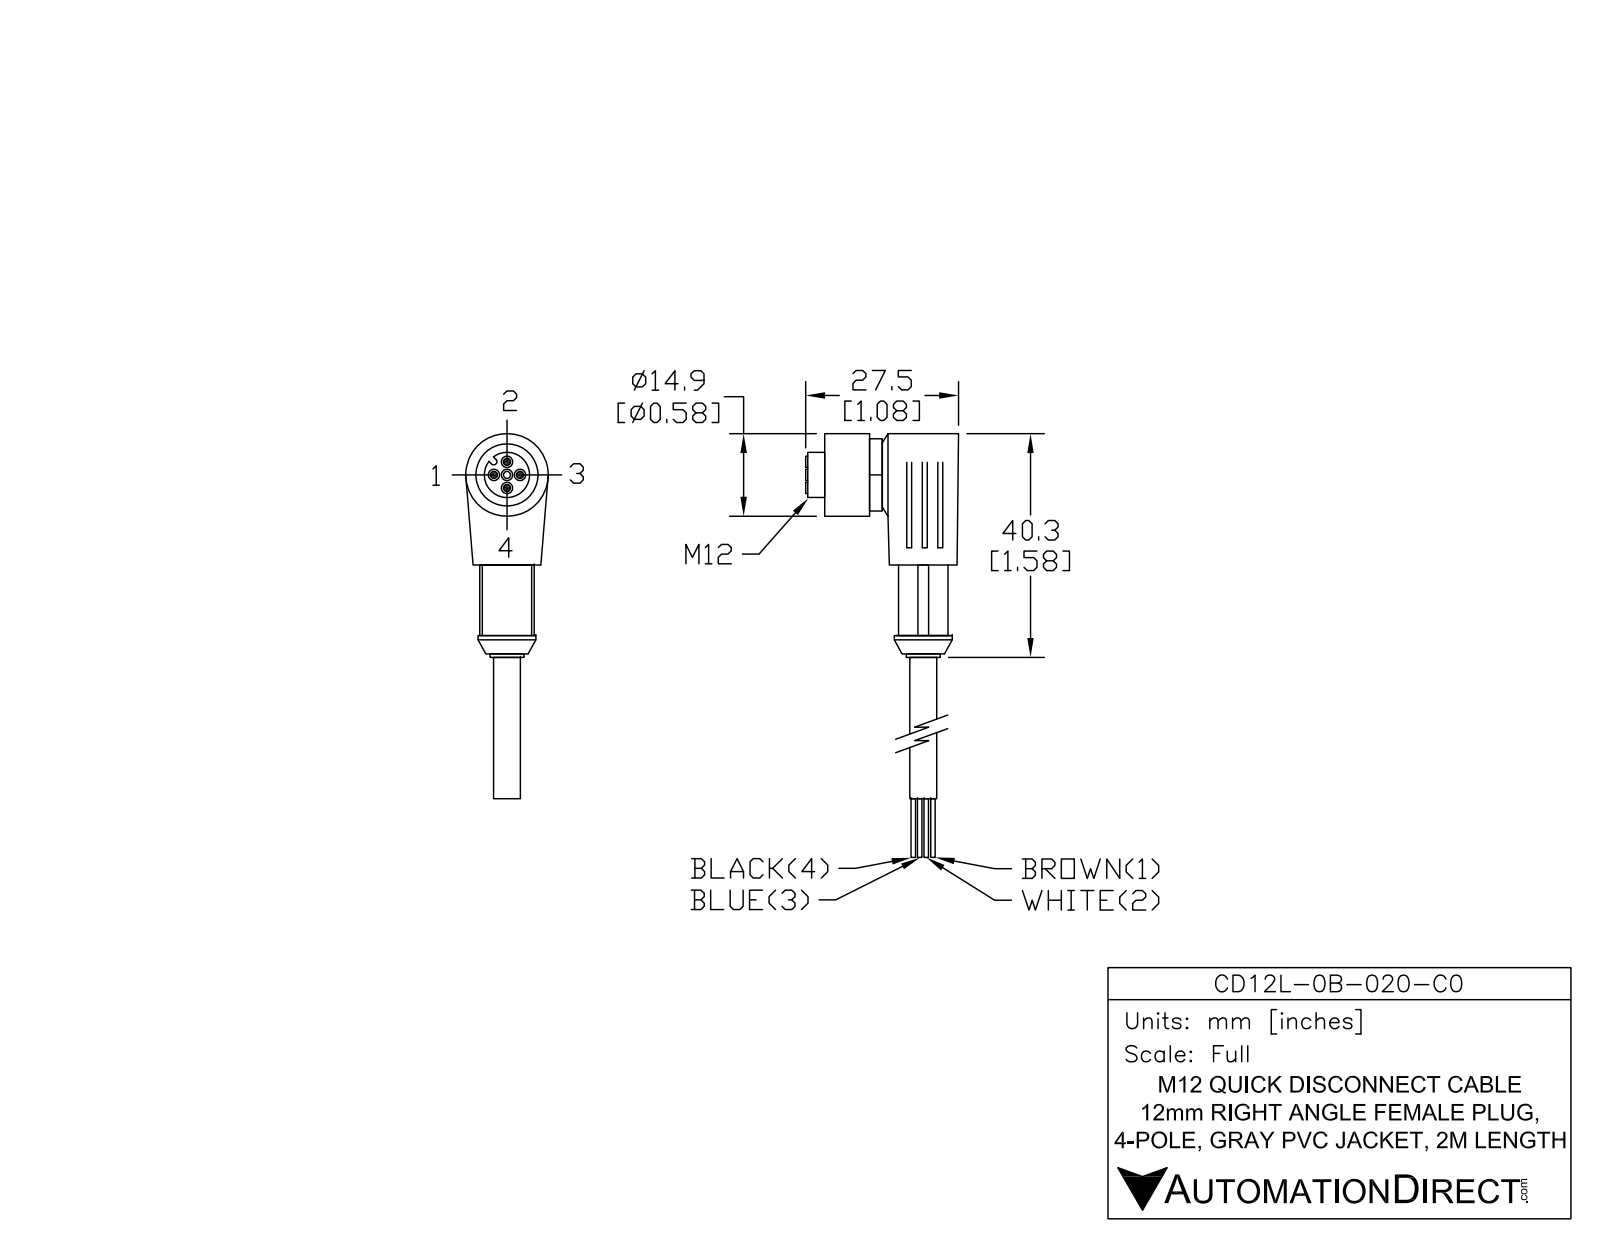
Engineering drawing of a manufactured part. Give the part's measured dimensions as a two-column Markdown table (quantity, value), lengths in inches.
| quantity | value |
| --- | --- |
| part name | CD12L-0B-020-C0 |
| STEP written by | SolidWorks 2017 (AUTOMOTIVE_DESIGN) |
| units | inches |
| bodies | 4 solids, 326 faces (218 planar, 106 cylindrical, 2 other) |
| overall size | 5.524 × 1.083 × 0.587 |
| volume | 0.52 in³ |
| surface area | 8.517 in² |
| round holes (diameter × count) | 0.039 × 5, 0.335 × 1, 0.472 × 1 |
| round bosses / shafts (diameter × count) | 0.587 × 1, 0.409 × 1, 0.343 × 1, 0.319 × 1, 0.193 × 1 |
| partial cylindrical surfaces (radius × count) | 0.022 × 1 |
| main face-to-face distances | 0.539, 0.5, 0.039, 0.055, 0.594, 0.094, 0.657, 0.232, 1.008, 0.508 |
| hole center spacings | 0.093, 0.131, 0.185 |
